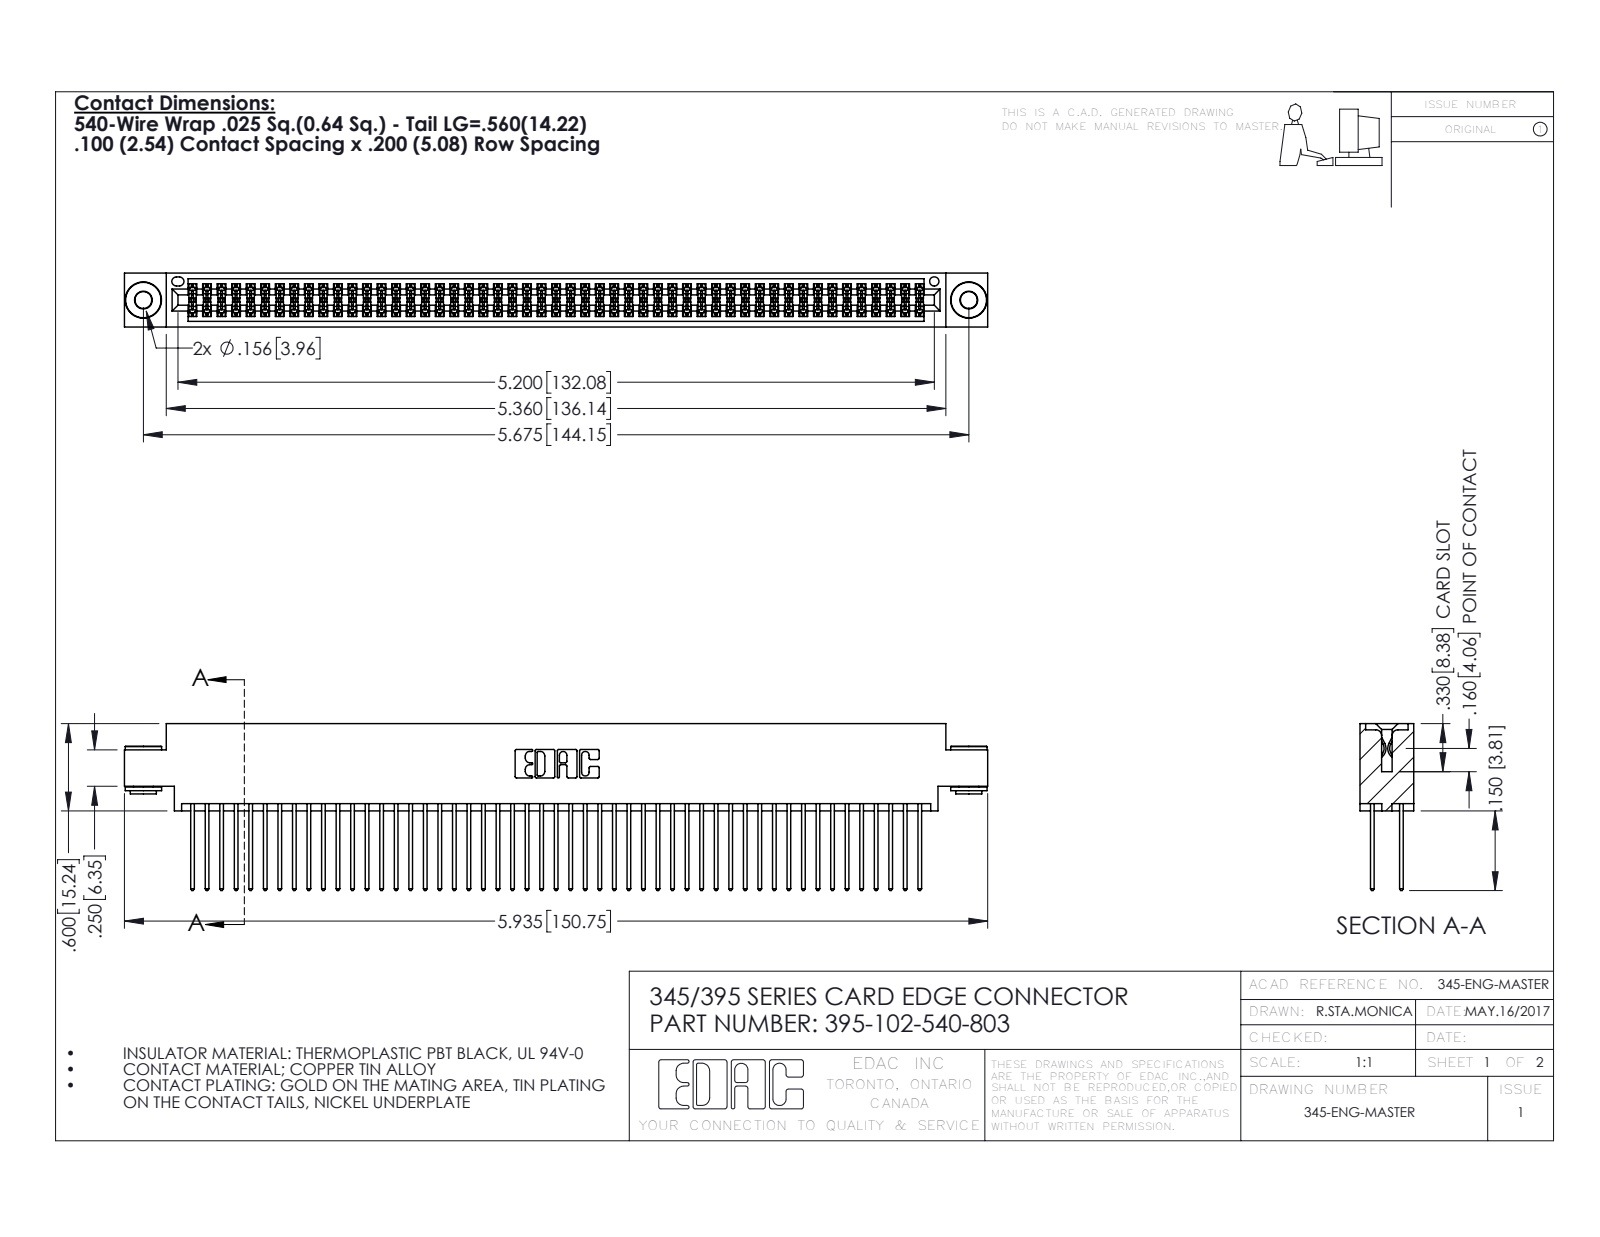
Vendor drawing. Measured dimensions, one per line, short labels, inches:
name: 345 Part_0.170 Offset - 0.156 Dia-TH; 395-102-540-803; 345-292-001_345-293-140; 345-250-002_345-250-002-102
written by: SolidWorks 2016 (CONFIG_CONTROL_DESIGN)
unit: in
bodies: 105 solids, 5268 faces (3460 planar, 1800 cylindrical, 8 other)
size: 5.935 × 1.147 × 0.37
volume: 0.917 in³; area: 38 in²
holes: 2× ⌀0.116, 2× ⌀0.156, 1× ⌀0.064
bosses: 2× ⌀0.25, 2× ⌀0.18, 2× ⌀0.136
rounds: 153× R0.006, 102× R0.01, 22× R0.01, 6× R0.007, 6× R0.031, 3× R0.026, 2× R0.014, 2× R0.019
face distances: 0.072, 0.298, 0.2, 0.098, 0.272, 0.025, 0.37, 0.225, 0.175, 0.149
hole spacings: 0.27, 5.439, 5.675
